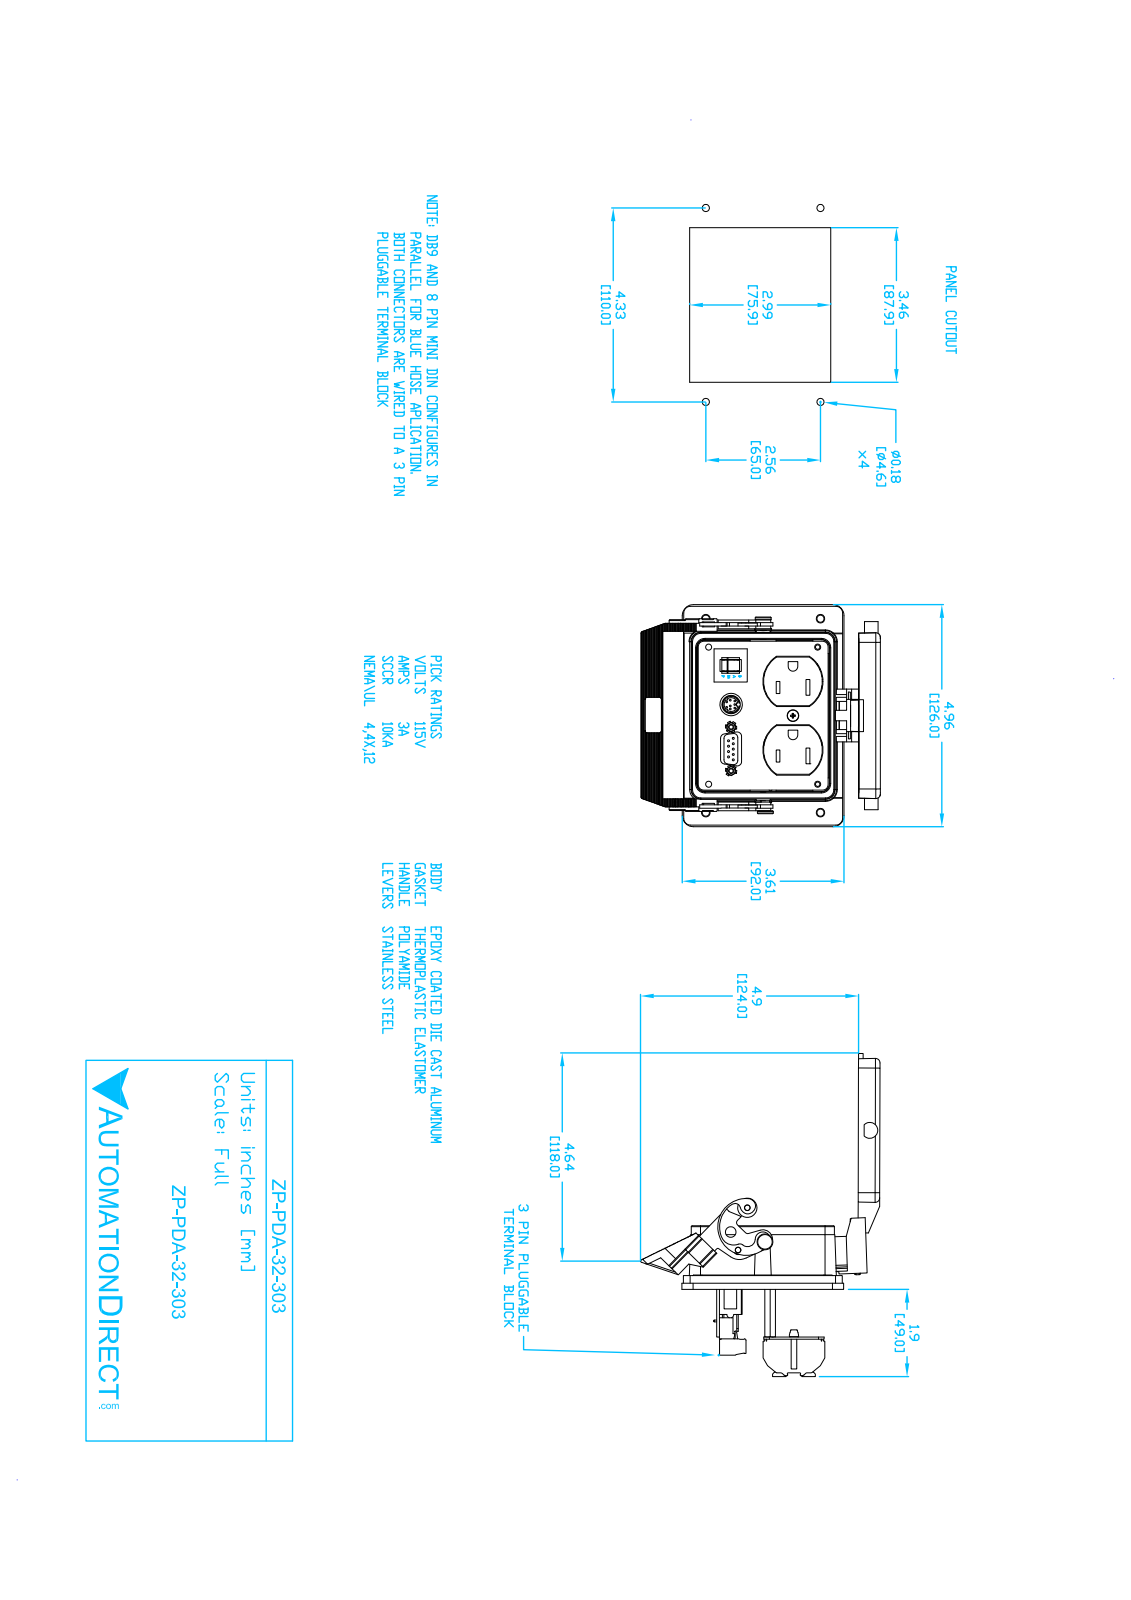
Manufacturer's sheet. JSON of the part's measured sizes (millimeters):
{"part_name": "ZP-PDA-32-303", "step_written_by": "SolidWorks 2017 (AUTOMOTIVE_DESIGN)", "units": "millimeters", "bodies": {"solids": 1, "faces": 3808, "planar": 2596, "cylindrical": 806, "other": 406}, "overall_size": [174.2, 135, 126], "volume_mm3": 221900, "surface_area_mm2": 127500, "round_holes": [[1.1, 9], [1, 8], [2.5, 8], [3.7, 8], [4.1, 7], [4.4, 6], [4.8, 4], [2.2, 3], [2.3, 3], [3, 3], [3.2, 3], [1.4, 2]], "round_bosses_or_shafts": [[0.6, 7], [5.7, 6], [5.6, 6], [3, 6], [5.2, 3], [3.6, 3], [0.3, 3], [9, 2]], "partial_cylinders_radius": [[0.5, 24], [2.5, 22], [0.6, 15], [6.4, 12], [1.2, 10], [0.4, 9], [0.4, 8], [3.2, 8]], "face_to_face_distances": [3.4, 1.3, 22.7, 41.3, 21.4, 92.8, 89.4, 18.5, 40, 24.8], "hole_center_spacings": [3, 16.1, 3.2, 5, 6.1, 12, 65.5, 94]}
